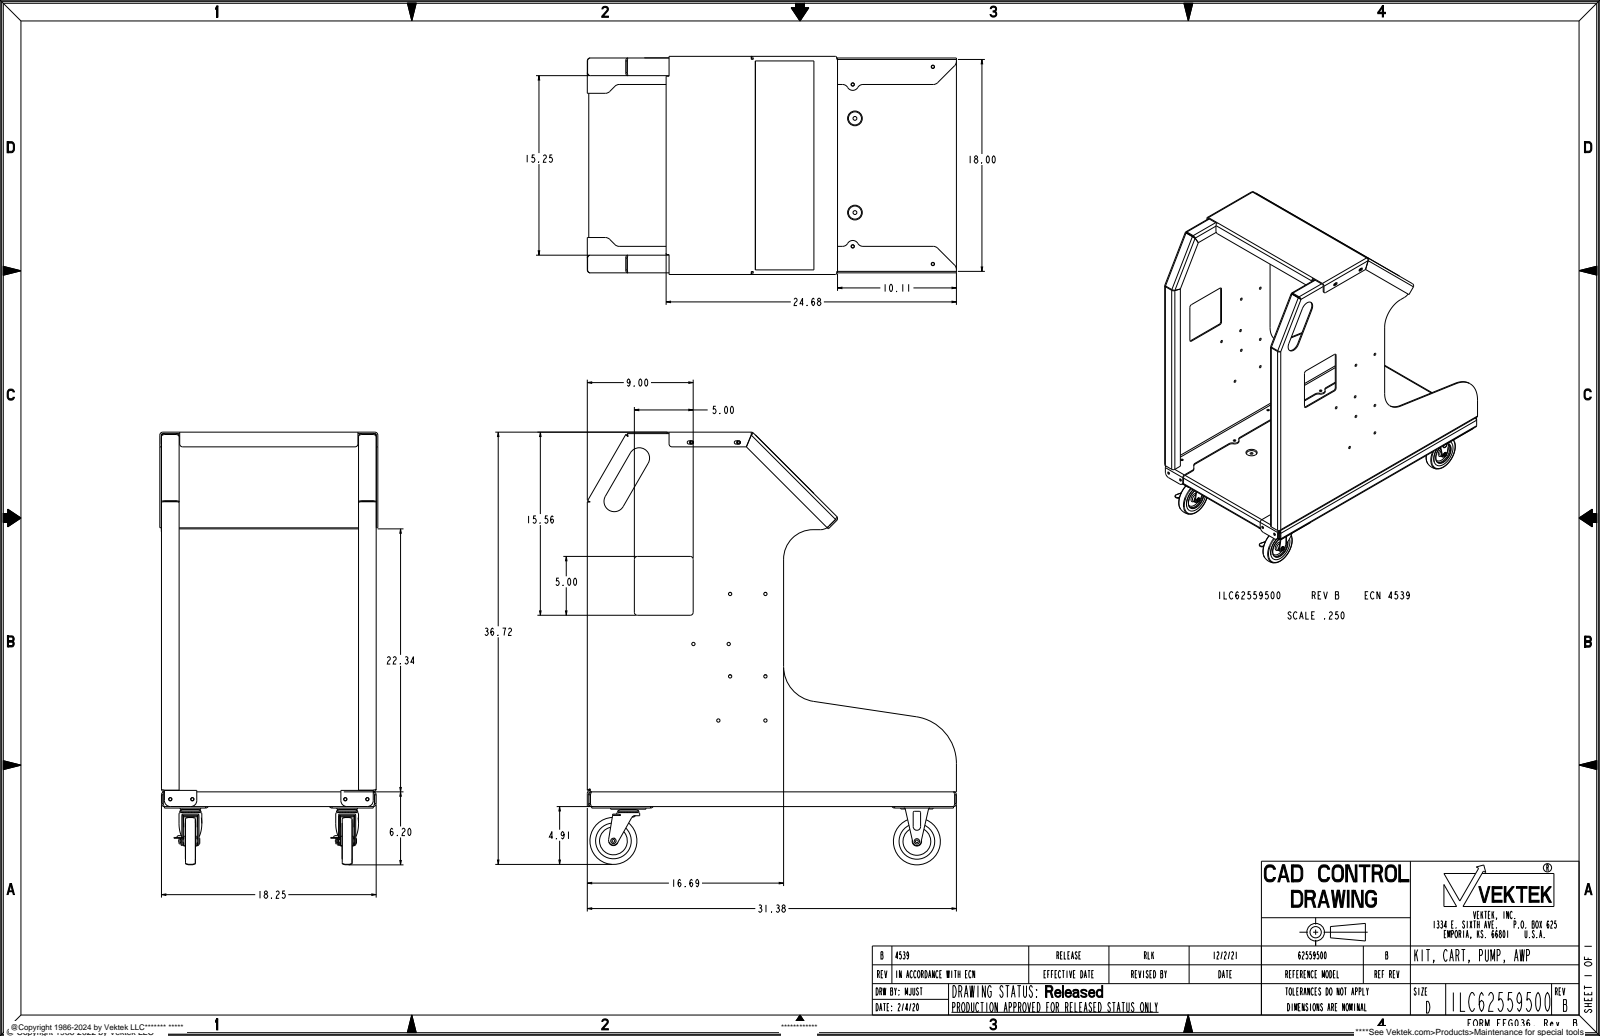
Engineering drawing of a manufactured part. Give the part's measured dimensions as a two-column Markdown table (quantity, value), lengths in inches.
| quantity | value |
| --- | --- |
| part name | ILC62559500 |
| STEP written by | PRO/ENGINEER BY PARAMETRIC TECHNOLOGY CORPORATION, 2017170 (AUTOMOTIVE_DESIGN) |
| units | inches |
| bodies | 0 solids, 1175 faces (505 planar, 362 cylindrical, 308 other) |
| overall size | 36.773 × 31.387 × 18.885 |
| round holes (diameter × count) | 0.8 × 4, 1.25 × 4, 0.328 × 2, 2.362 × 2 |
| round bosses / shafts (diameter × count) | 0.25 × 9, 0.567 × 7, 1.795 × 2, 1.181 × 2, 0.795 × 2, 0.428 × 2, 0.512 × 1 |
| partial cylindrical surfaces (radius × count) | 0.125 × 49, 0.25 × 44, 0.059 × 12, 0.118 × 12, 0.197 × 12, 0.472 × 10, 0.079 × 9, 0.394 × 8 |
| main face-to-face distances | 0.125, 18.125, 0.12, 18, 18.25, 1.13, 0.245, 1.25, 16.75, 1.01 |
| hole center spacings | 2.5, 8, 14, 16.124, 16.75, 16.935, 5.927, 5.929 |
